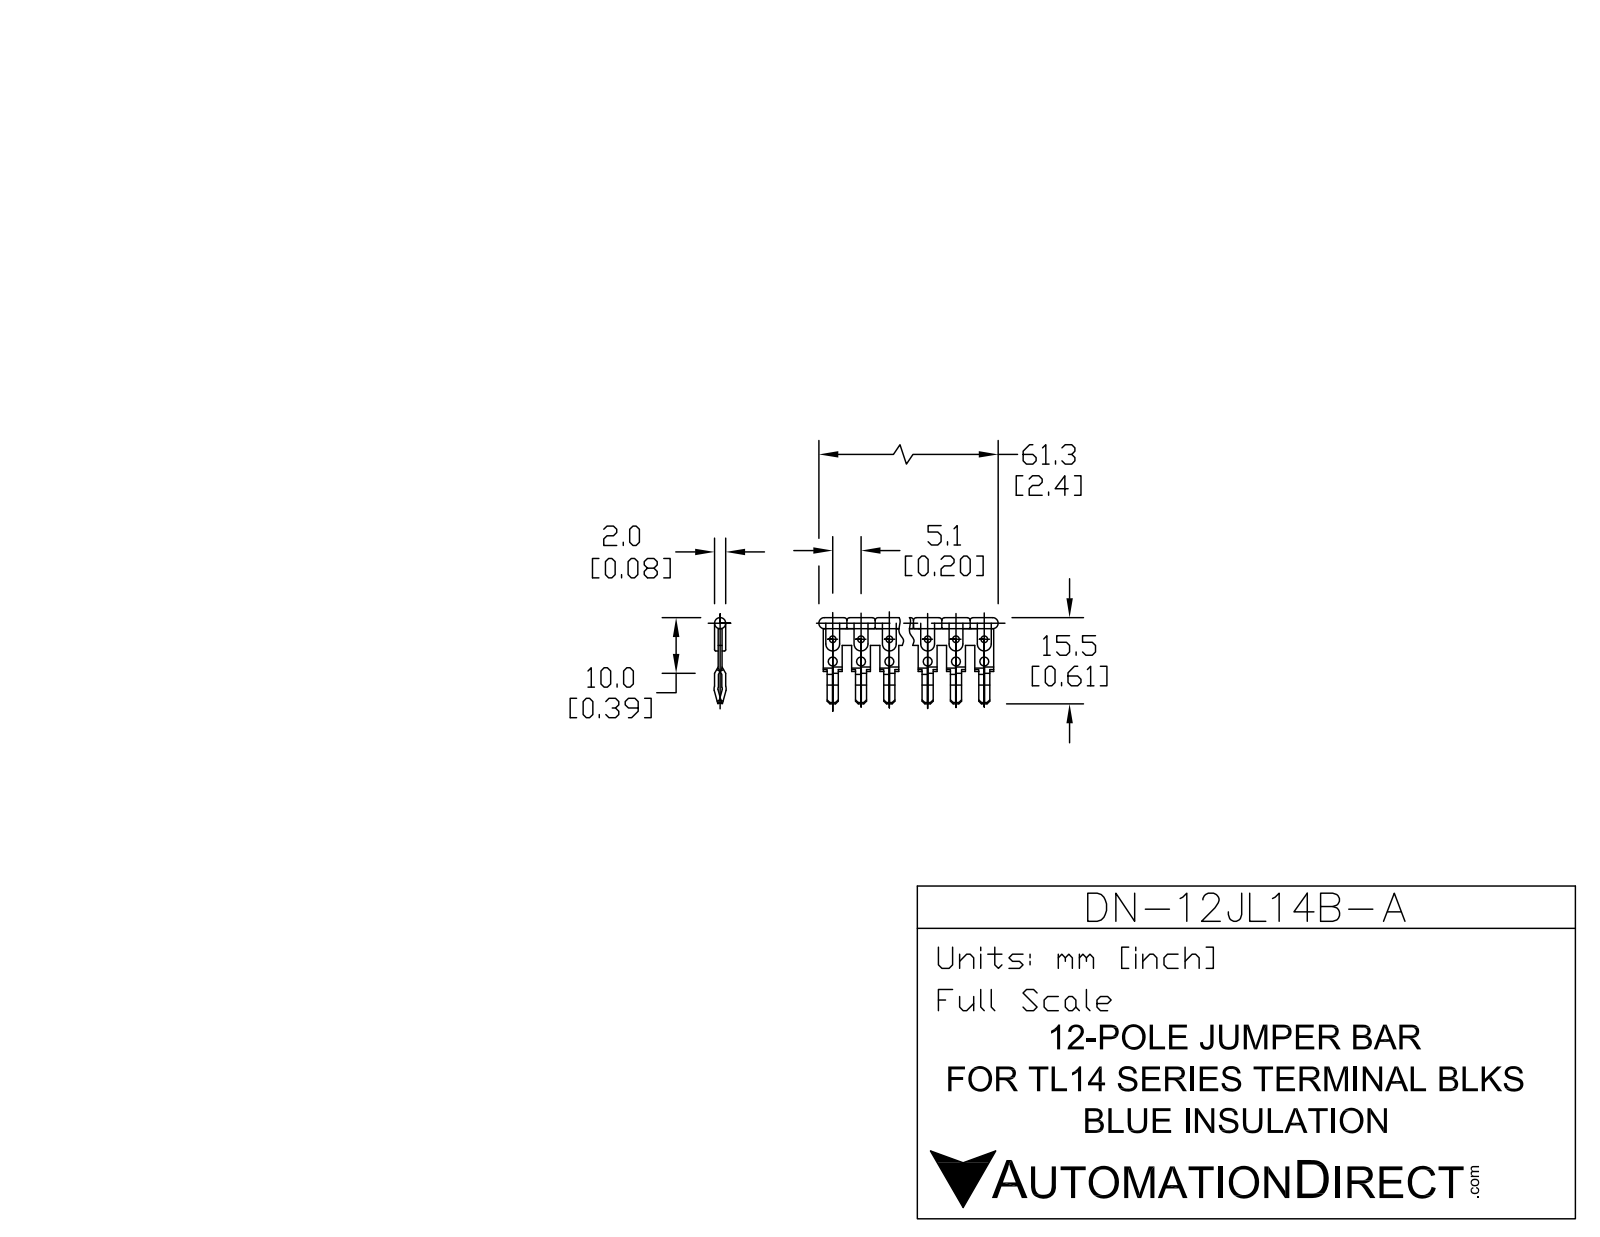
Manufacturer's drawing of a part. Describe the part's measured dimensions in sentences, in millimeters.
The part is named "43531_12_BLS_DN-12JL14B-A". Its 3-D file was written by "SolidWorks 2013 (AUTOMOTIVE_DESIGN)". It is 2 solids with 847 faces: 419 planar, 332 cylindrical and 96 other. Overall it measures 61.1 by 15.5 by 2.08 millimeters. Its volume is 756 cubic millimeters and its surface area 2 220 square millimeters. Round holes: 12 of diameter 1.2, 12 of diameter 1.3. Round bosses or shafts: 1 of diameter 2. Partial cylindrical surfaces (rounded edges, fillets, slot ends): 48 of radius 0.25, 12 of radius 1.25, 4 of radius 0.48, 4 of radius 0.7, 3 of radius 0.5. The main face-to-face distances are 0.7, 0.65, 1.35, 0.55, 2, 1.9, 1.25, 0.8, 1.2, 1.1. The hole center spacings are 5.1, 6.48, 10.2, 10.96, 15.3, 15.81, 20.4, 20.79.
